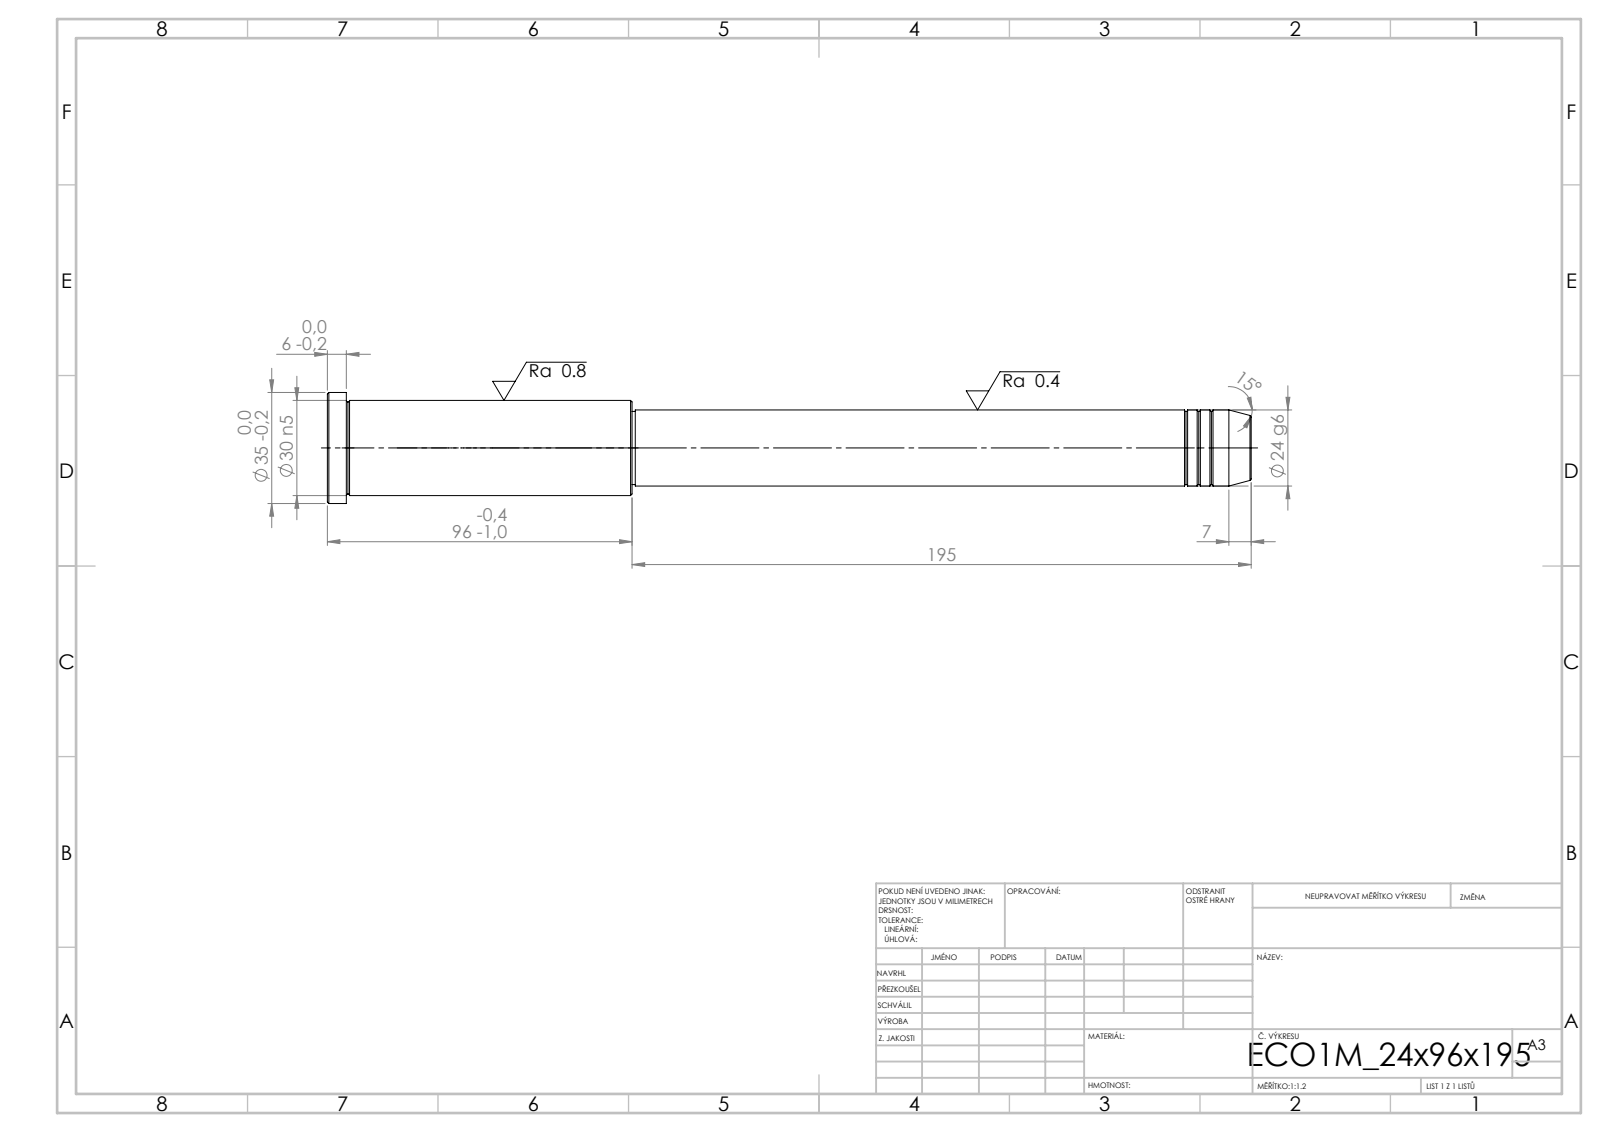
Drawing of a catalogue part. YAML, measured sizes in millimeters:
step_written_by: "SolidWorks 2019 (CONFIG_CONTROL_DESIGN)"
units: millimeters
bodies: {solids: 1, faces: 43, planar: 5, cylindrical: 14, other: 24}
overall_size: [291, 35, 35]
volume: 156949
surface_area: 25788
round_bosses_or_shafts:
  - {diameter: 35, count: 1}
  - {diameter: 30, count: 1}
  - {diameter: 24, count: 1}
  - {diameter: 23, count: 1}
face_to_face_distances: [291, 285, 6, 195, 90, 96, 194, 1, 91, 97]
